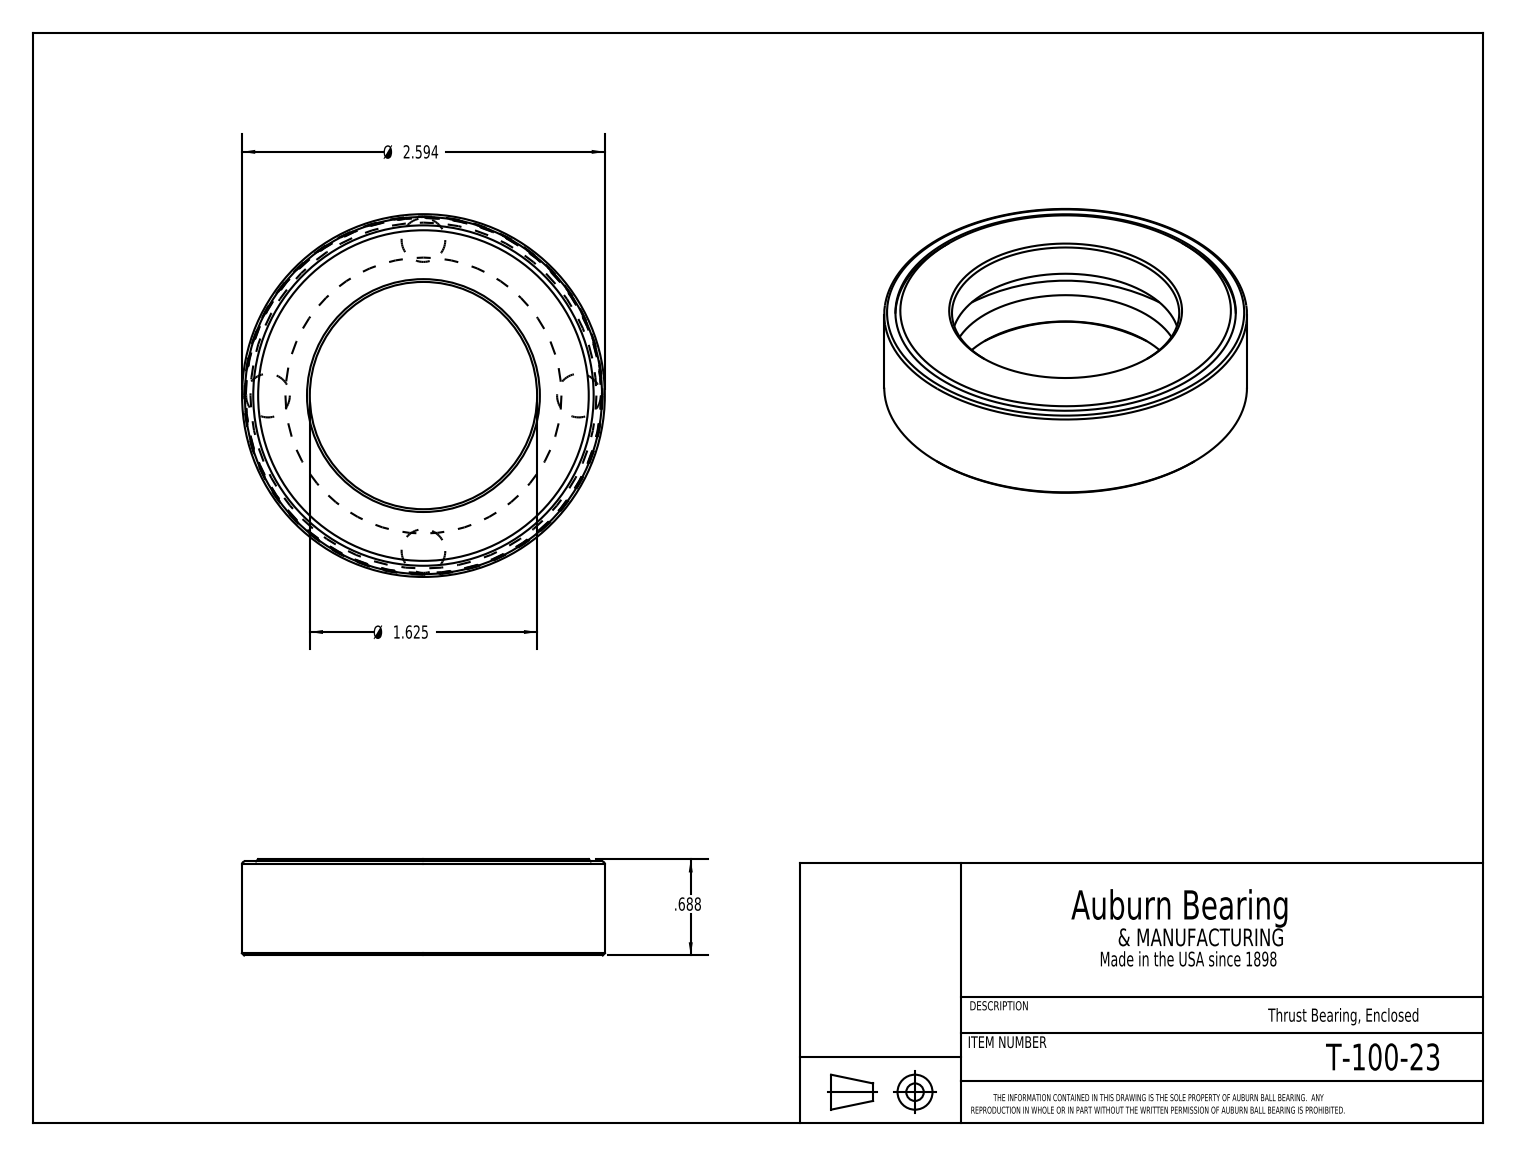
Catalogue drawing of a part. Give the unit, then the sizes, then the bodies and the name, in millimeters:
Units: millimetres
Overall size (bounding box): 65.9 × 65.9 × 17.5
Round holes (diameter × count): ⌀41.3 ×1, ⌀61.8 ×1, ⌀64.9 ×1
Round bosses / shafts (diameter × count): ⌀65.9 ×1, ⌀64.5 ×1
Main face-to-face distances: 6.4, 11.1, 17.4, 4.7, 16.6, 10.2, 5.5, 0.9, 17.1, 10.7
Volume: 24 680 mm³ · Surface area: 18 010 mm²
Bodies: 6 solids, 28 faces (9 planar, 7 cylindrical, 12 other)
Part name (STEP PRODUCT): T-100-23
STEP written by: SolidWorks 2016 (CONFIG_CONTROL_DESIGN)
